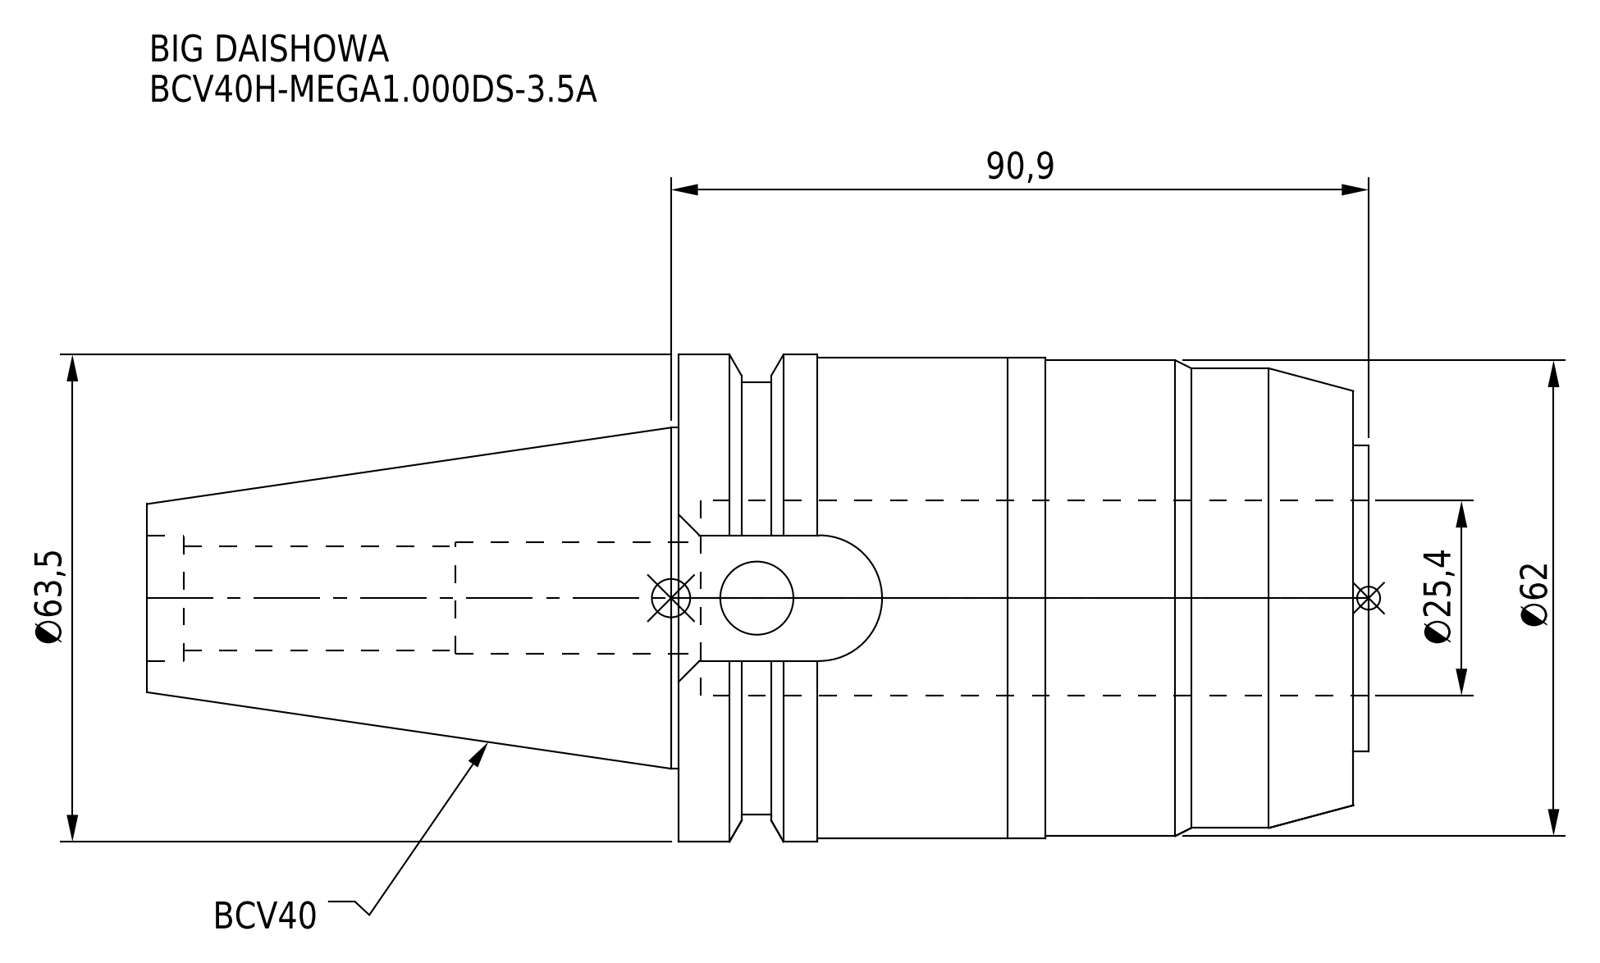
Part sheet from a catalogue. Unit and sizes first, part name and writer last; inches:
Units: inches
Overall size (bounding box): 6.266 × 2.5 × 2.469
Round holes (diameter × count): ⌀0.375 ×1, ⌀0.535 ×1, ⌀0.571 ×1, ⌀0.643 ×1, ⌀1 ×1
Round bosses / shafts (diameter × count): ⌀2.5 ×1, ⌀2.469 ×1, ⌀2.441 ×1, ⌀2.358 ×1, ⌀2.219 ×1, ⌀1.75 ×1, ⌀1.571 ×1
Partial cylindrical surfaces — rounded edges, fillets, slot ends (radius × count): R0.322 ×1
Main face-to-face distances: 3.461, 0.079, 3.539, 3.425, 3.346, 0.114, 1.872, 6.266, 6.187, 2.841
Volume: 16.34 in³ · Surface area: 62.78 in²
Bodies: 1 solid, 65 faces (25 planar, 30 cylindrical, 10 other)
Part name (STEP PRODUCT): BCV40H-MEGA1_000DS-3_5A
STEP written by: CREO PARAMETRIC BY PTC INC, 2016380 (AUTOMOTIVE_DESIGN)
